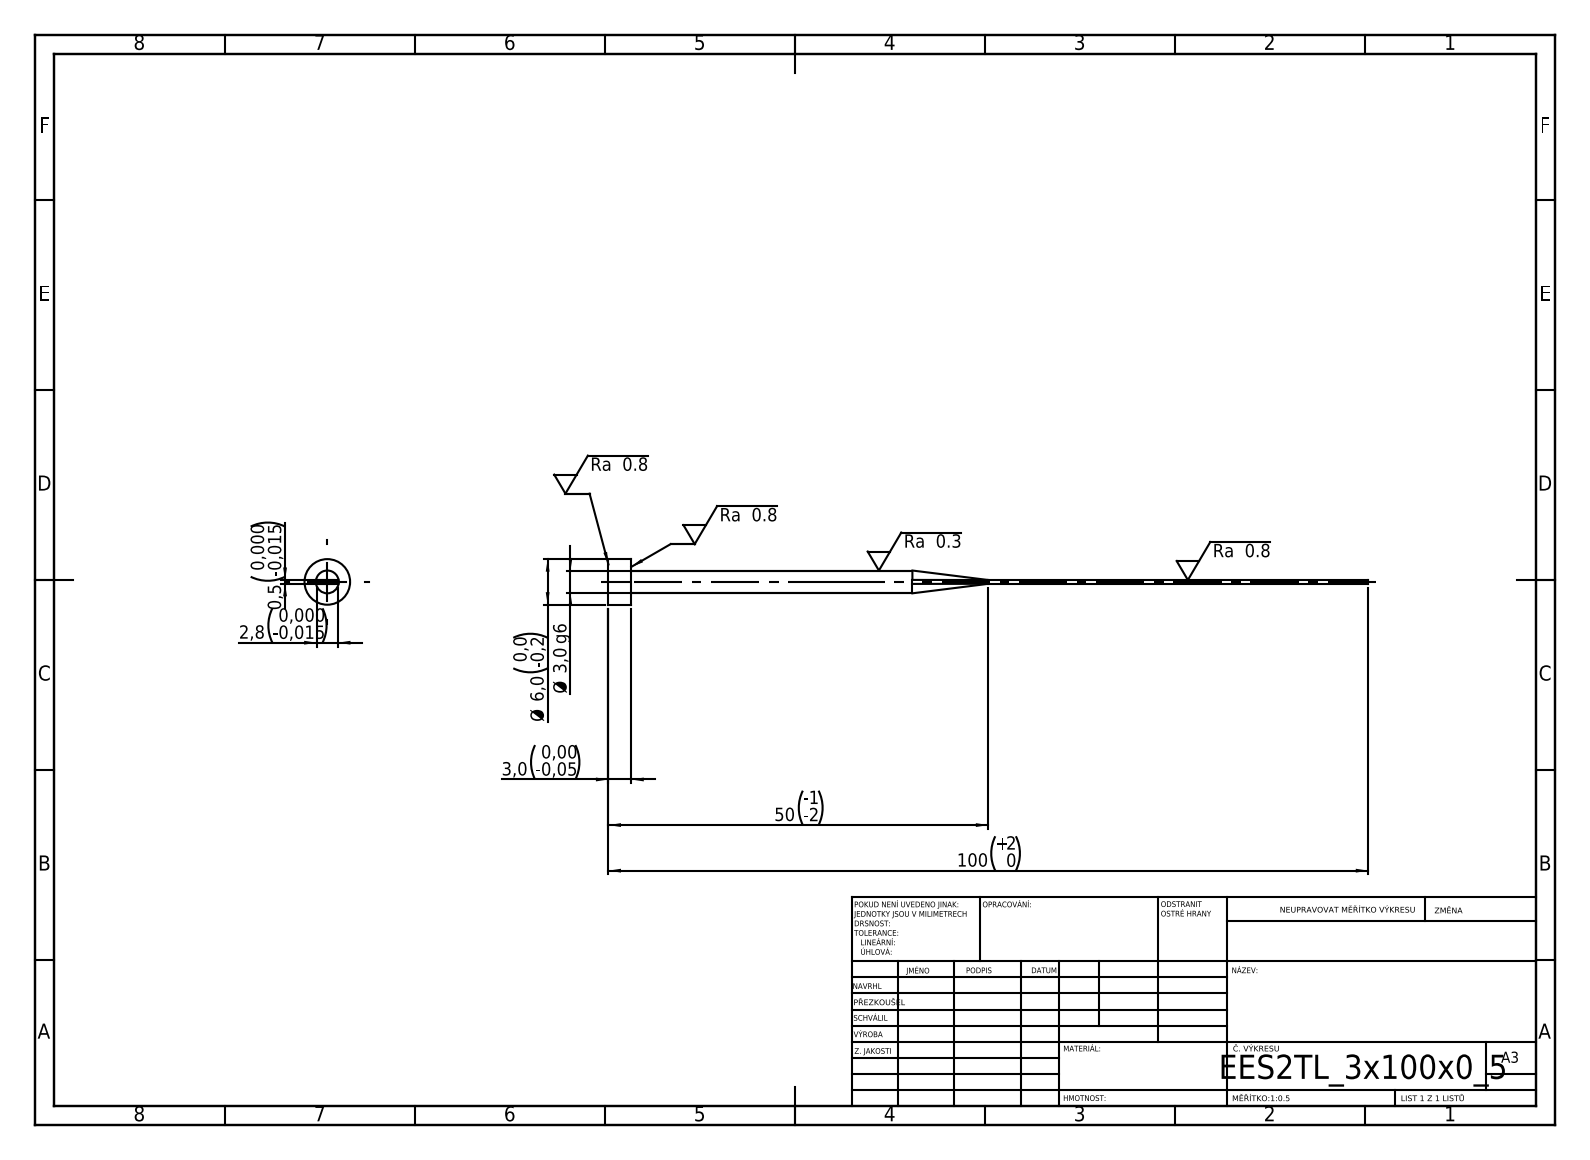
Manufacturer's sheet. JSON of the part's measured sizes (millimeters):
{"step_written_by": "SolidWorks 2019 (CONFIG_CONTROL_DESIGN)", "units": "millimeters", "bodies": {"solids": 1, "faces": 15, "planar": 7, "cylindrical": 4, "other": 4}, "overall_size": [100, 6, 6], "volume_mm3": 456, "surface_area_mm2": 863, "round_bosses_or_shafts": [[6, 1], [3, 1]], "face_to_face_distances": [0.5, 2.8, 3, 100, 97]}
